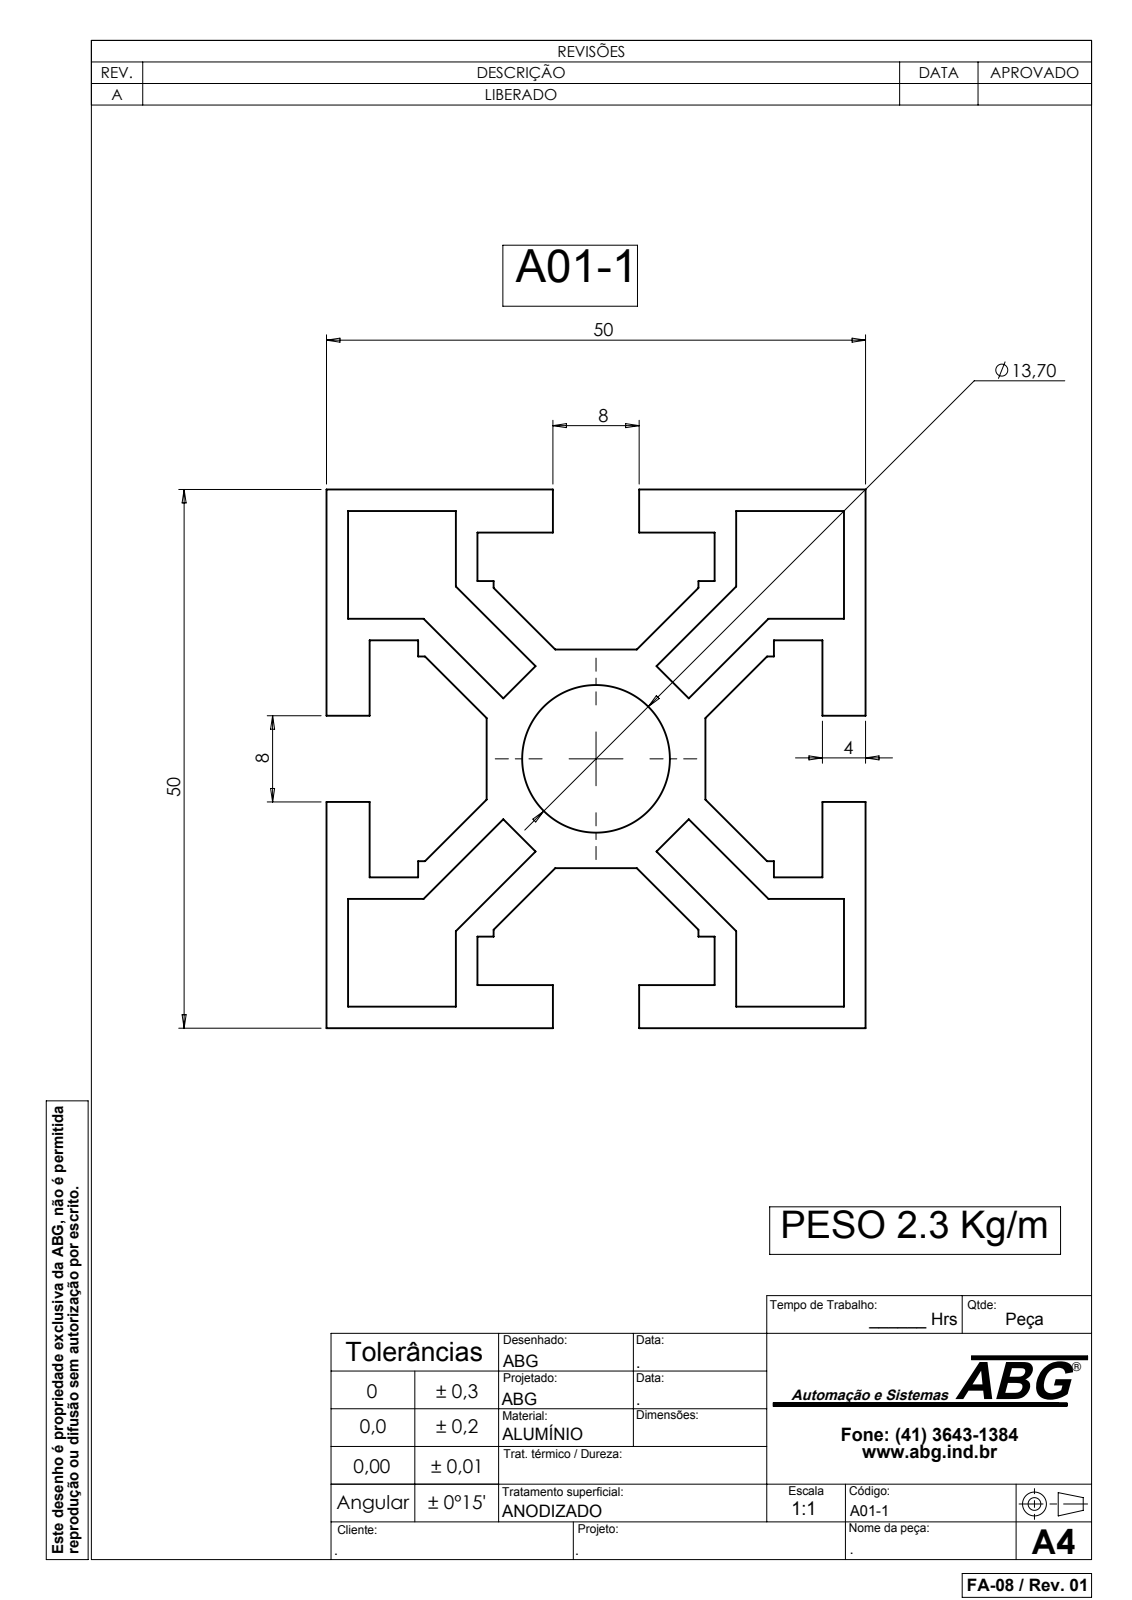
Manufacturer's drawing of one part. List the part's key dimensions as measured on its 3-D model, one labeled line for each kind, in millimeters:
Part name (STEP PRODUCT): A01-1
STEP written by: SolidWorks 2007 (CONFIG_CONTROL_DESIGN)
Units: millimetres
Bodies: 1 solid, 92 faces (90 planar, 2 cylindrical, 0 other)
Overall size (bounding box): 6000 × 50 × 50
Volume: 5 504 000 mm³ · Surface area: 4 104 000 mm²
Round holes (diameter × count): ⌀13.7 ×1
Main face-to-face distances: 2, 46, 12, 36, 10, 34, 50, 48, 8, 2.38
